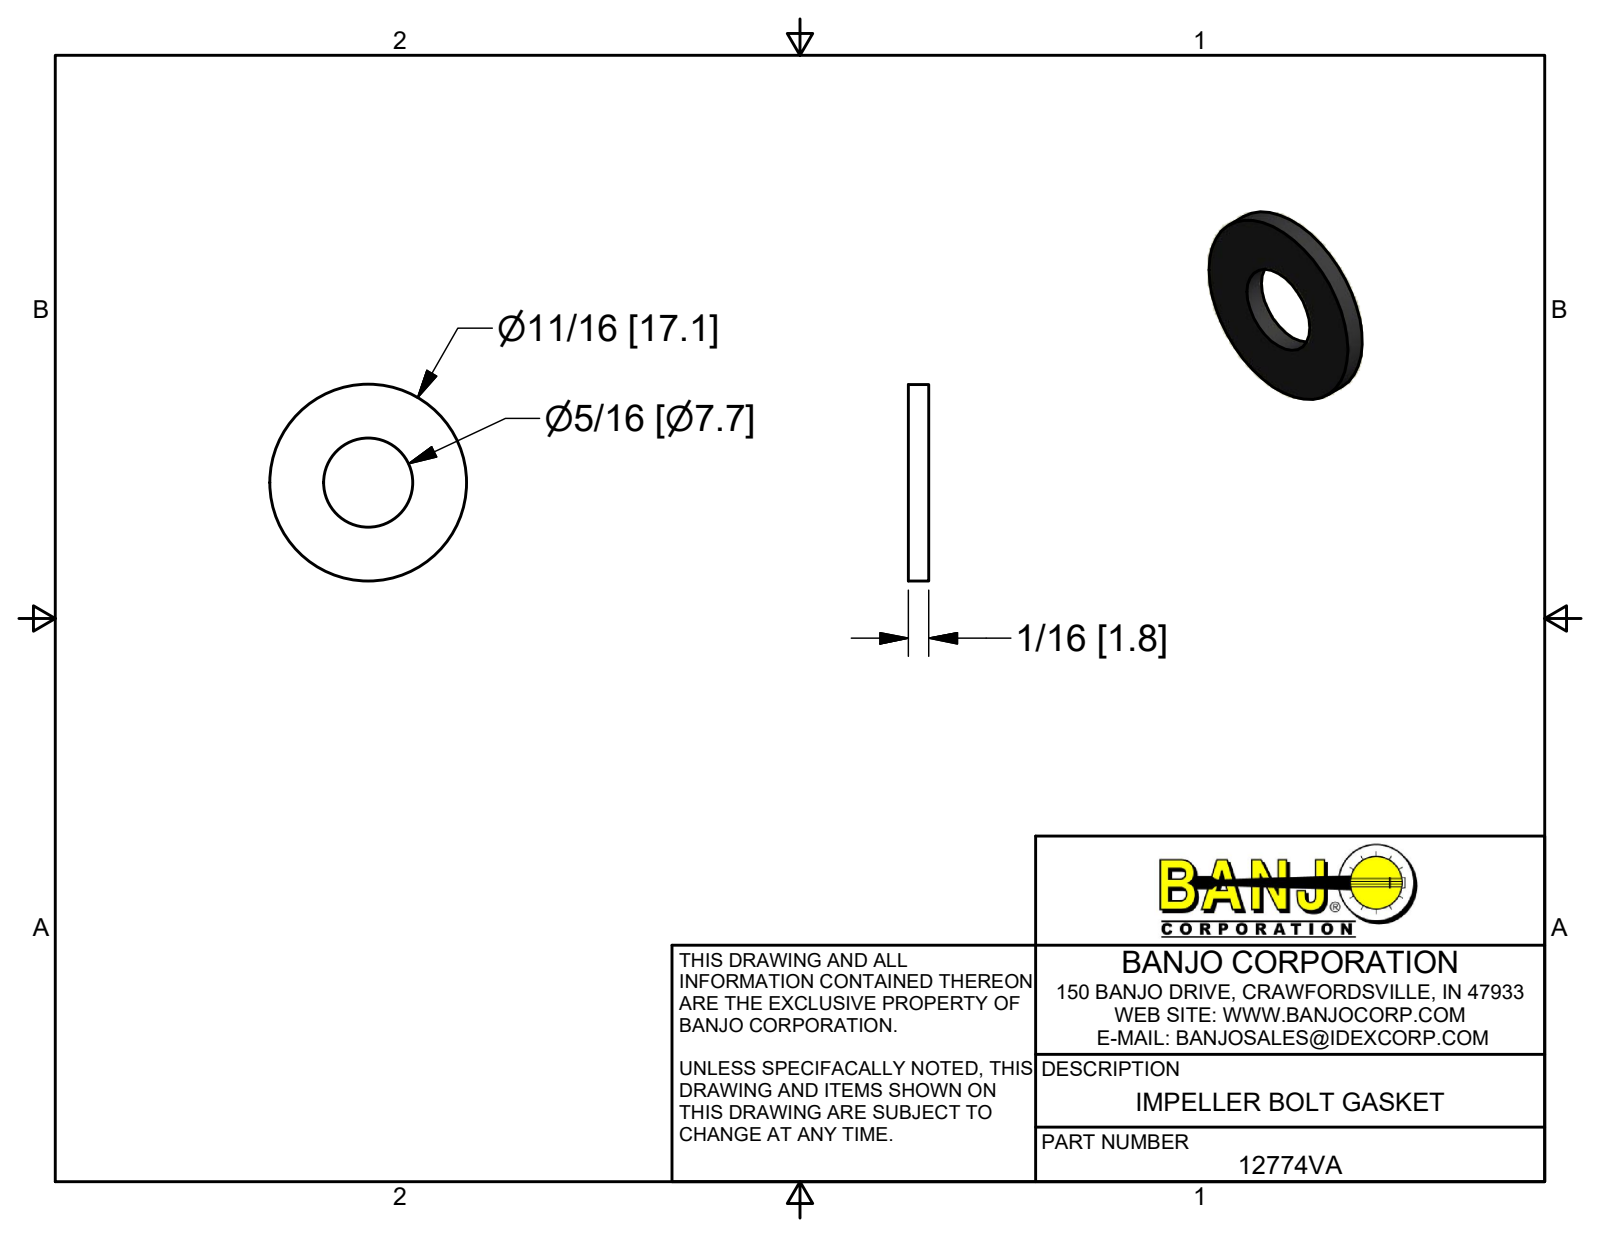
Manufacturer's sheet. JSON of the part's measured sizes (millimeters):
{"part_name": "12774VA", "step_written_by": "Autodesk Inventor 2017 (AUTOMOTIVE_DESIGN)", "units": "millimeters", "bodies": {"solids": 1, "faces": 4, "planar": 2, "cylindrical": 2, "other": 0}, "overall_size": [17.14, 17.14, 1.78], "volume_mm3": 327, "surface_area_mm2": 506, "round_holes": [[7.75, 1]], "round_bosses_or_shafts": [[17.14, 1]], "face_to_face_distances": [1.78]}
